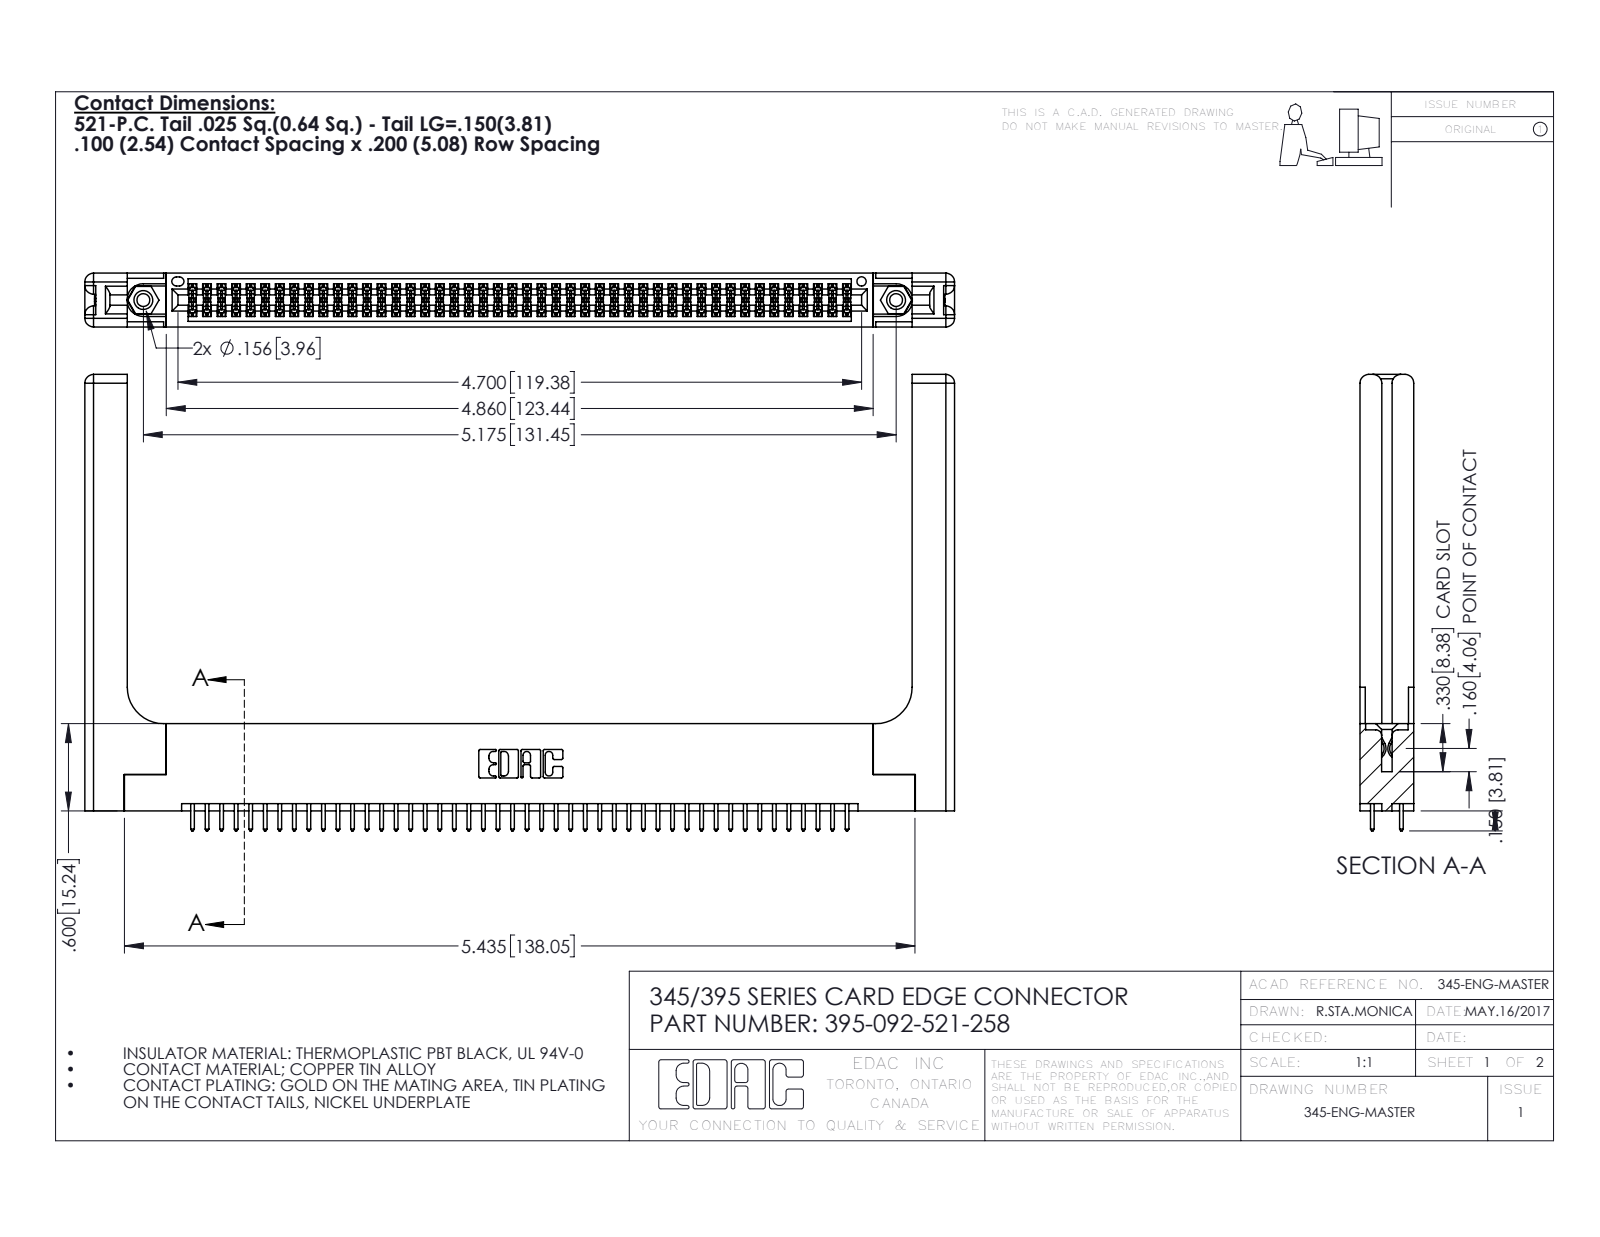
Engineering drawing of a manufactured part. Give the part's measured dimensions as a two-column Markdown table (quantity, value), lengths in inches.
| quantity | value |
| --- | --- |
| part name | 345-292-001_345-293-121; 345-220-058_345-220-058; 395-092-521-258; 345-250-001_345-250-001-102 (+1 more) |
| STEP written by | SolidWorks 2016 (CONFIG_CONTROL_DESIGN) |
| units | inches |
| bodies | 97 solids, 4982 faces (3264 planar, 1658 cylindrical, 60 other) |
| overall size | 5.979 × 3.137 × 0.37 |
| volume | 1.417 in³ |
| surface area | 41.38 in² |
| round holes (diameter × count) | 0.089 × 2, 0.125 × 2, 0.156 × 2, 0.064 × 1 |
| round bosses / shafts (diameter × count) | 0.155 × 2 |
| partial cylindrical surfaces (radius × count) | 0.006 × 138, 0.01 × 92, 0.01 × 22, 0.06 × 16, 0.007 × 6, 0.031 × 6, 0.026 × 3, 0.014 × 2 |
| main face-to-face distances | 0.072, 0.298, 0.37, 0.2, 0.098, 0.272, 0.025, 0.225, 0.148, 0.15 |
| hole center spacings | 0.27, 4.939, 5.175 |
